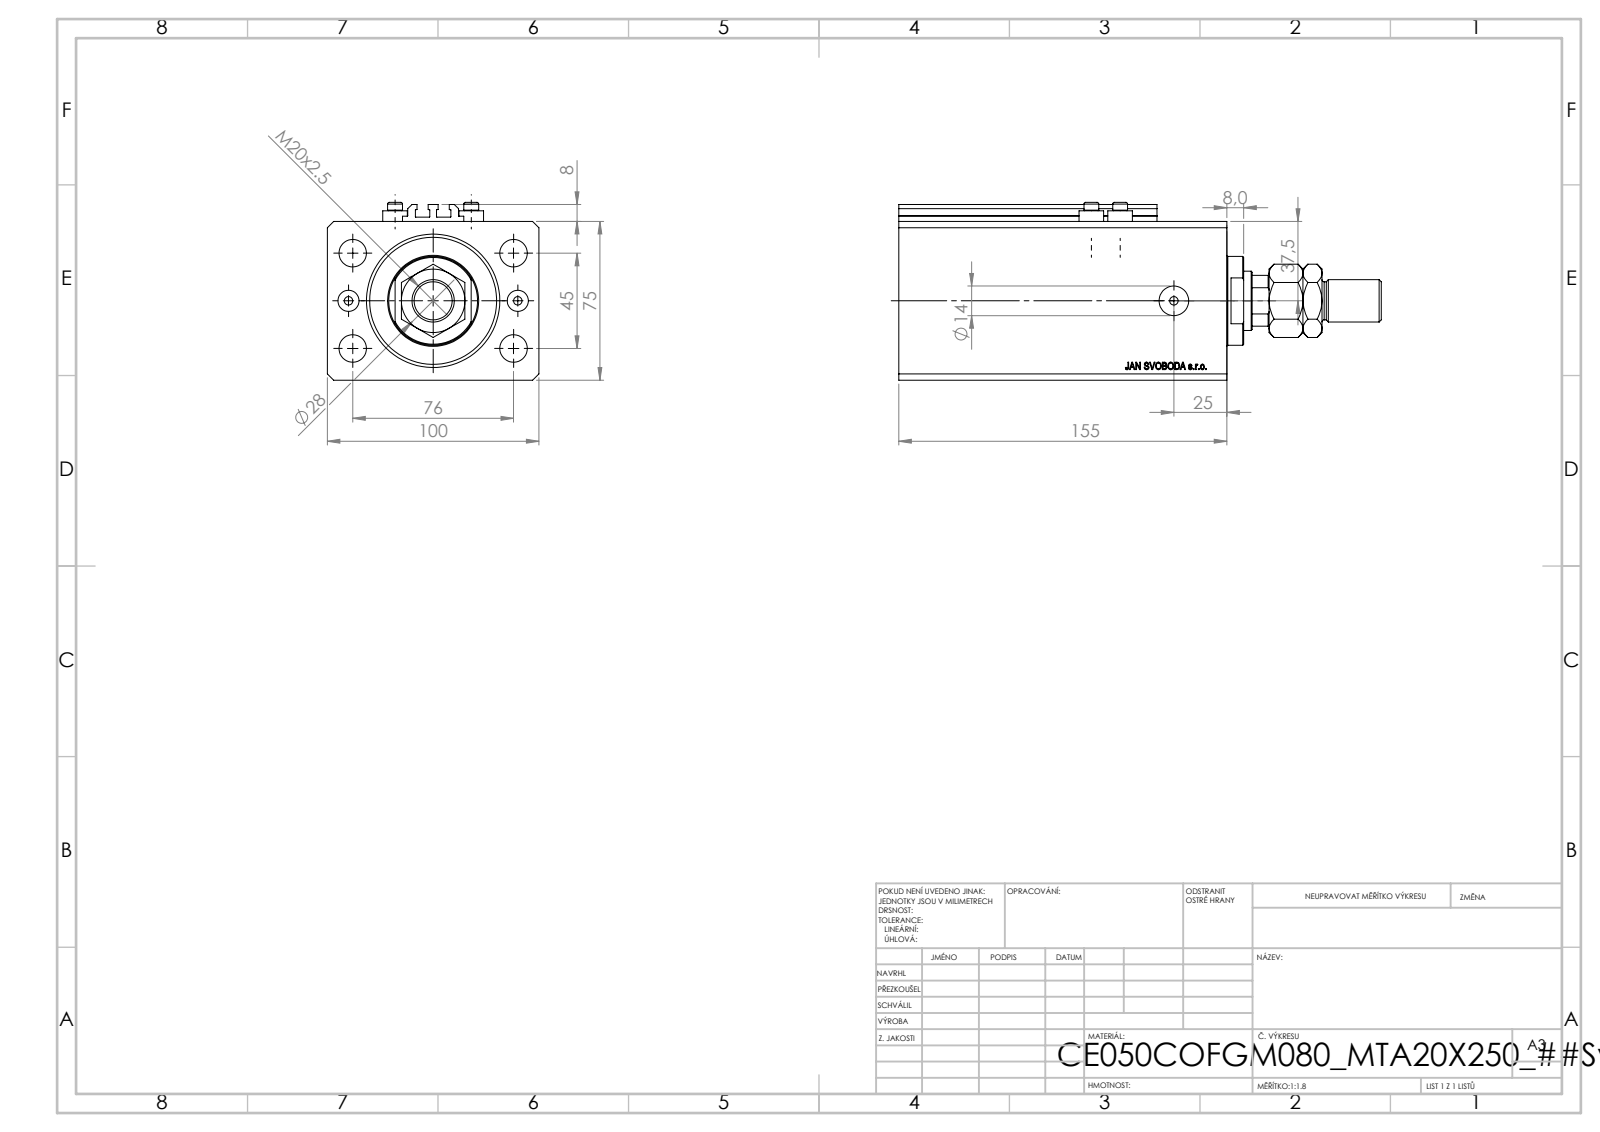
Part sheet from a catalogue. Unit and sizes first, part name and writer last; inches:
Units: inches
Overall size (bounding box): 8.976 × 3.937 × 3.307
Round holes (diameter × count): ⌀0.157 ×8, ⌀0.512 ×4, ⌀0.394 ×2, ⌀0.551 ×2, ⌀0.728 ×1, ⌀1.102 ×1, ⌀1.969 ×1, ⌀2.48 ×1
Round bosses / shafts (diameter × count): ⌀0.457 ×4, ⌀0.276 ×4, ⌀1.654 ×1, ⌀0.787 ×1, ⌀0.709 ×1
Partial cylindrical surfaces — rounded edges, fillets, slot ends (radius × count): R0.008 ×10, R0.531 ×1
Main face-to-face distances: 2.953, 3.937, 6.102, 0.787, 0.469, 5.634, 5.315, 4.846, 0.118, 3.15
Hole centre spacings: 0.889, 1.739, 3.196, 0.535, 1.417, 1.515, 1.575, 1.772
Volume: 62.24 in³ · Surface area: 269.6 in²
Bodies: 9 solids, 1083 faces (519 planar, 90 cylindrical, 474 other)
Part name (STEP PRODUCT): V250CE_VC_C; ALLEN BOLT V250CE; MTA; V250CE_C_VCP (+1 more)
STEP written by: SolidWorks 2019 (CONFIG_CONTROL_DESIGN)
